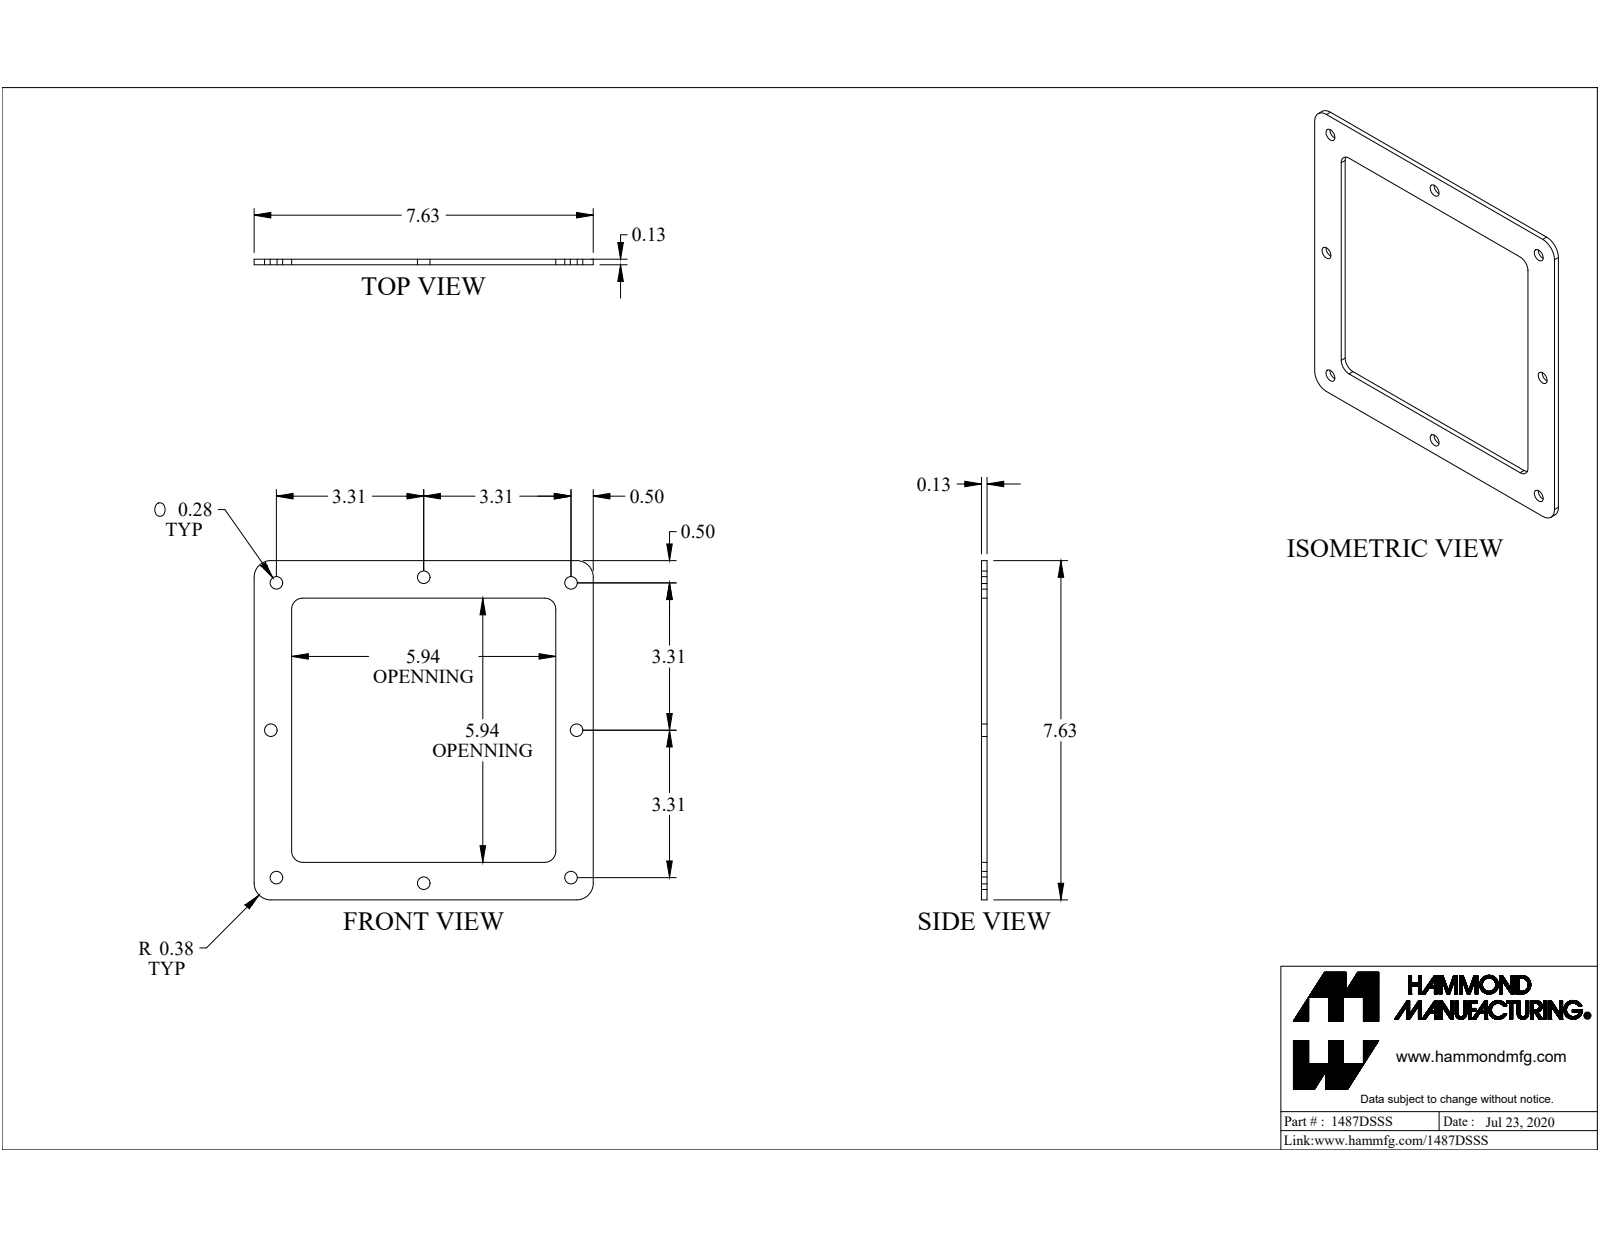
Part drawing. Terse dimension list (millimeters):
name: 1487DSSS
written by: SolidWorks 2019 (CONFIG_CONTROL_DESIGN)
unit: mm
bodies: 1 solid, 26 faces (10 planar, 16 cylindrical, 0 other)
size: 193.7 × 193.7 × 3.2
volume: 45 690 mm³; area: 33 640 mm²
holes: 8× ⌀7.1
rounds: 4× R6.4, 4× R9.5
face distances: 3.2, 21.4, 172.3, 193.7, 150.9
hole spacings: 84.2, 191, 123.5, 168.3, 174.6, 238
